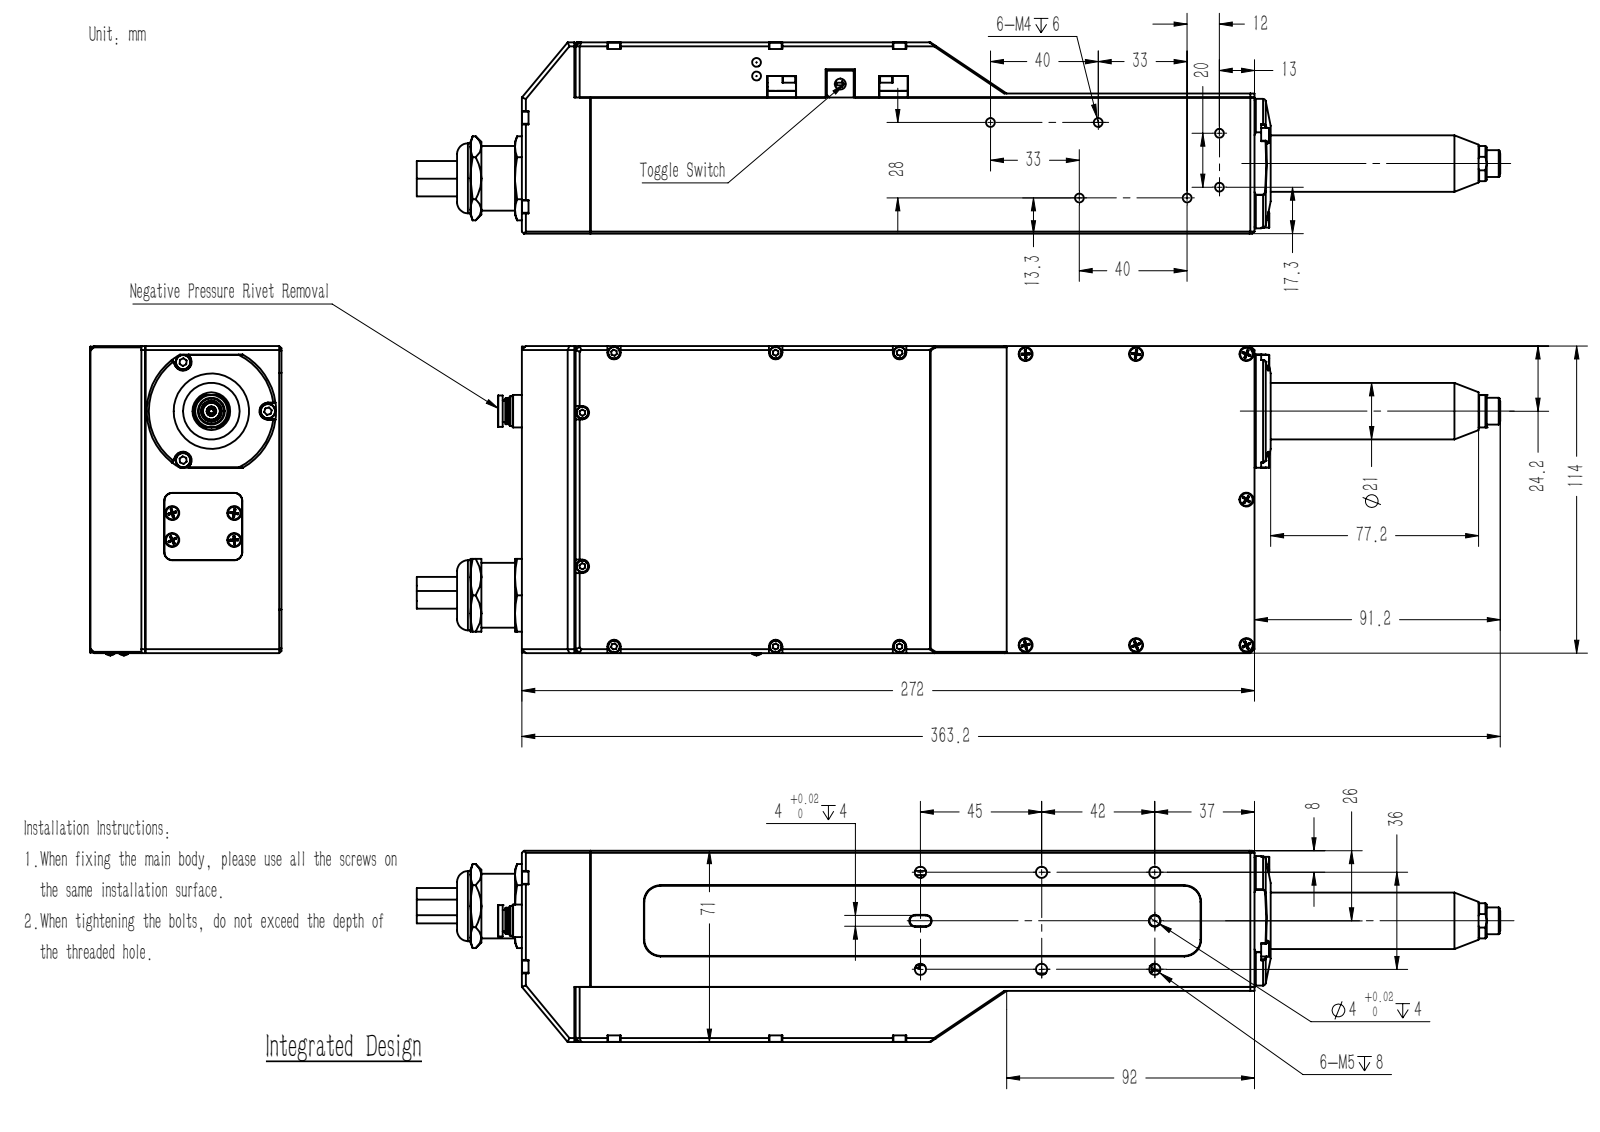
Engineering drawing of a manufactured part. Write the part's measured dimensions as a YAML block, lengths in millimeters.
part_name: "内六角圆柱头螺钉M3×10加弹垫; 内六角圆柱头螺钉M2.5×5; 十字槽沉头螺钉M2.5×6; 内六角圆柱头螺钉 M3×8 (+8 more)"
step_written_by: "SolidWorks 2019 (CONFIG_CONTROL_DESIGN)"
units: millimeters
bodies: {solids: 76, faces: 1985, planar: 857, cylindrical: 582, other: 546}
overall_size: [402.22, 114.8, 71]
volume: 1944000
surface_area: 228383
round_holes:
  - {diameter: 2.05, count: 22}
  - {diameter: 2.8, count: 17}
  - {diameter: 3.4, count: 13}
  - {diameter: 6, count: 11}
  - {diameter: 2.5, count: 6}
  - {diameter: 3.3, count: 6}
  - {diameter: 4.2, count: 6}
  - {diameter: 2.7, count: 4}
  - {diameter: 3, count: 4}
  - {diameter: 2.9, count: 2}
  - {diameter: 2, count: 1}
  - {diameter: 4, count: 1}
round_bosses_or_shafts:
  - {diameter: 2.5, count: 29}
  - {diameter: 5.5, count: 19}
  - {diameter: 4.7, count: 15}
  - {diameter: 3, count: 15}
  - {diameter: 2.16, count: 15}
  - {diameter: 4.5, count: 14}
  - {diameter: 1, count: 5}
  - {diameter: 6.6, count: 2}
partial_cylinders:
  - {radius: 3, count: 17}
  - {radius: 2, count: 16}
  - {radius: 0.2, count: 15}
  - {radius: 2.5, count: 12}
  - {radius: 0.5, count: 9}
  - {radius: 2.95, count: 4}
  - {radius: 6, count: 4}
  - {radius: 1.4, count: 2}
face_to_face_distances: [50.5, 71, 20.5, 1.5, 114, 52, 19, 5.5, 246.5, 252]
hole_center_spacings: [109, 18, 19.81, 41, 108, 115.52, 20.5, 25]
